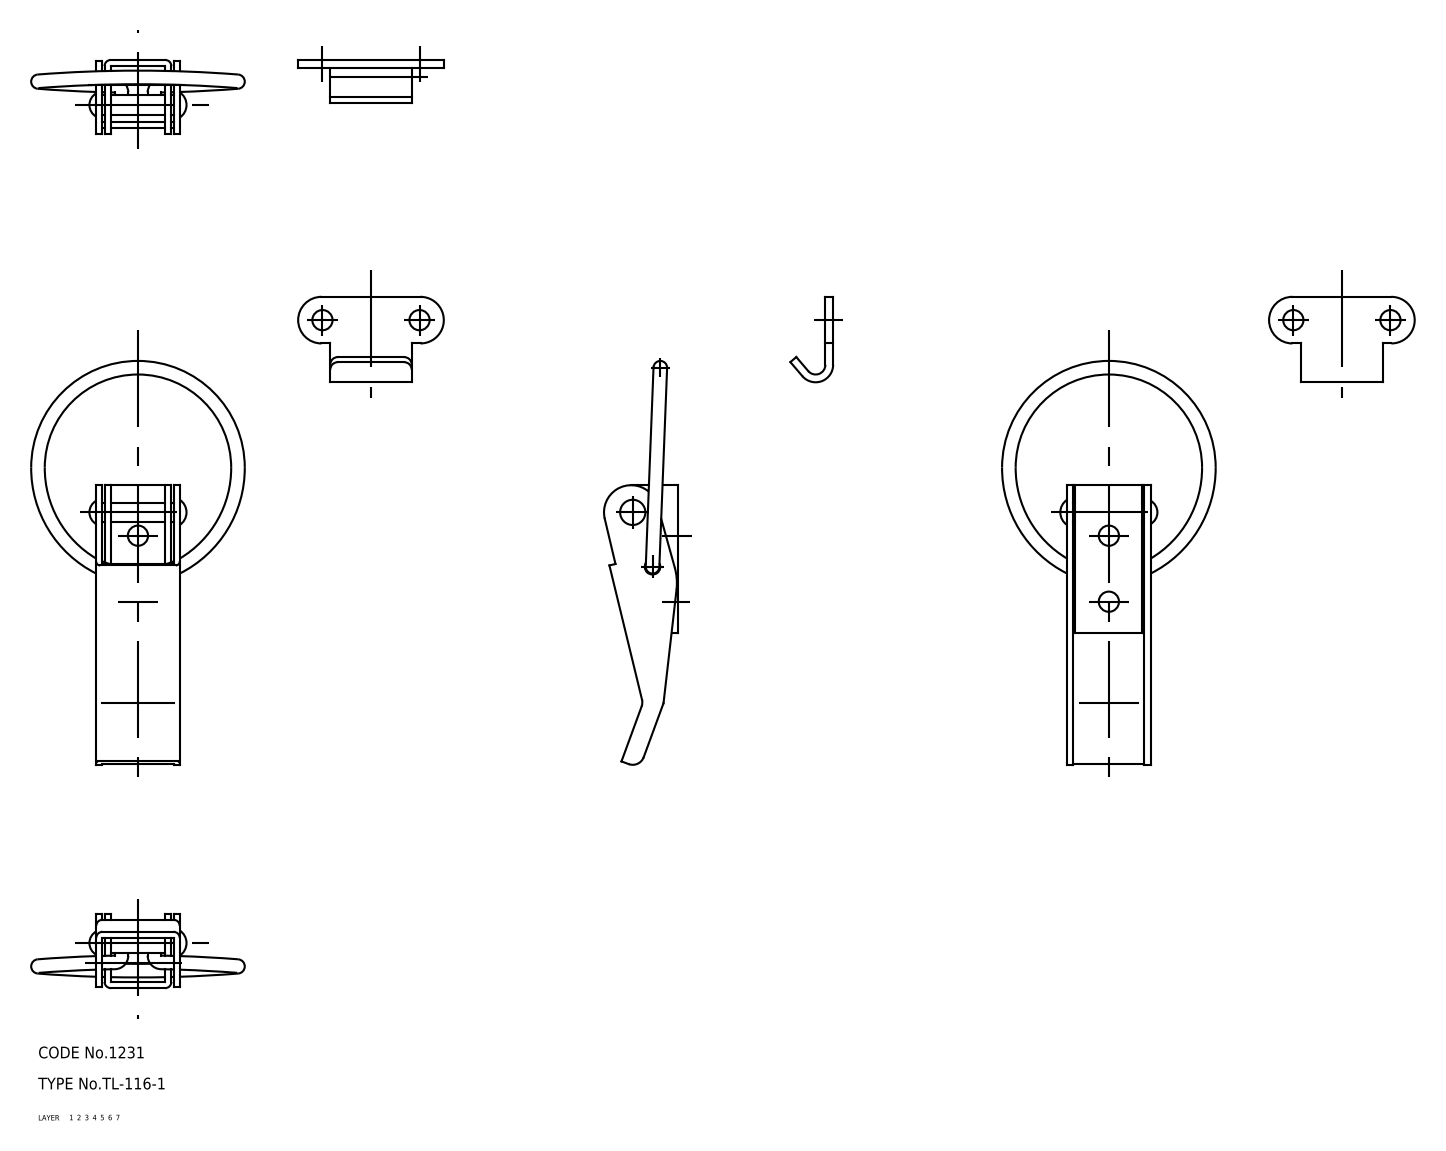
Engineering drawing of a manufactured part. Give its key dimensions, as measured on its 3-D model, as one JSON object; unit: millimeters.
{"part_name": "arm; shaft; lever; keeper (+2 more)", "step_written_by": "CADfix (AUTOMOTIVE_DESIGN)", "units": "millimeters", "bodies": {"solids": 5, "faces": 117, "planar": 0, "cylindrical": 0, "other": 117}, "overall_size": [120.5, 55, 19], "volume_mm3": 9247, "surface_area_mm2": 12039}
